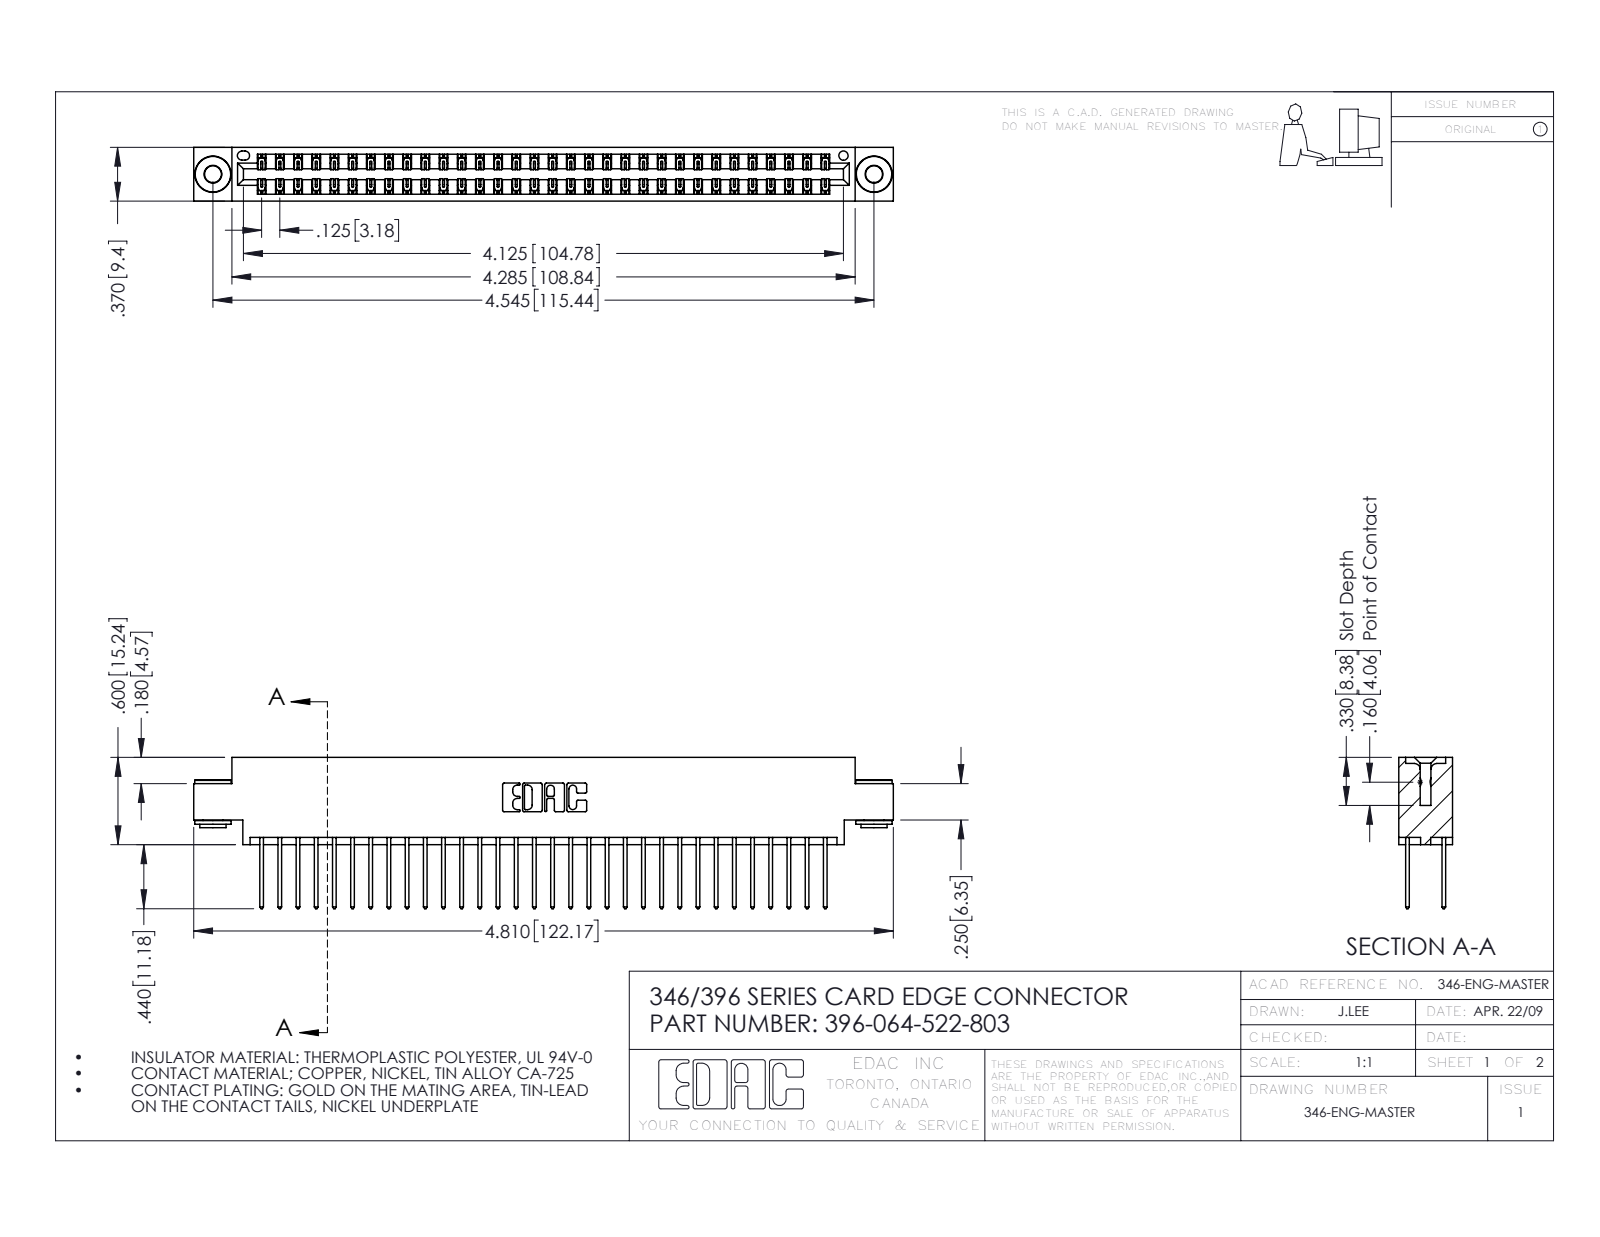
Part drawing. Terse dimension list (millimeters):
name: 345-250-002_345-250-002-102; 396-064-522-803; 346 Part_0.170 Offset - 0.156 Dia-TH; 345-292-001_345-293-122
written by: SolidWorks 2016 (CONFIG_CONTROL_DESIGN)
unit: mm
bodies: 67 solids, 3492 faces (2330 planar, 1154 cylindrical, 8 other)
size: 122.2 × 26.4 × 9.4
volume: 11 900 mm³; area: 17 300 mm²
holes: 2× ⌀2.9, 2× ⌀4, 1× ⌀1.6
bosses: 2× ⌀6.4, 2× ⌀4.6, 2× ⌀3.5
rounds: 96× R0.2, 64× R0.3, 22× R0.3, 6× R0.2, 6× R0.8, 3× R0.7, 2× R0.4, 2× R0.6
face distances: 1.2, 8.2, 6.4, 9.4, 0.6, 1.8, 7.6, 7, 3.8, 5.6
hole spacings: 6.2, 110.2, 115.4
